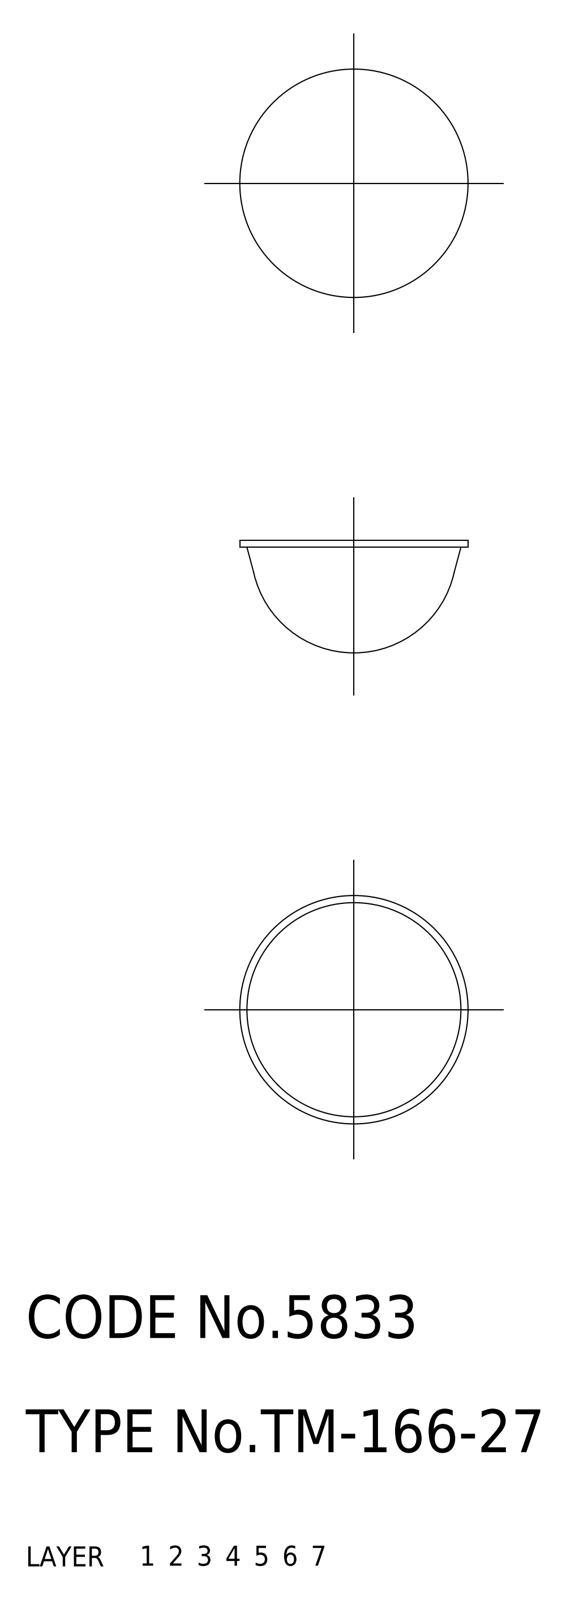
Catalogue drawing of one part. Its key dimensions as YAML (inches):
part_name: "rubber foot"
step_written_by: "CADfix (AUTOMOTIVE_DESIGN)"
units: inches
bodies: {solids: 1, faces: 7, planar: 0, cylindrical: 0, other: 7}
overall_size: [0.63, 0.63, 0.311]
volume: 0.056
surface_area: 0.913
